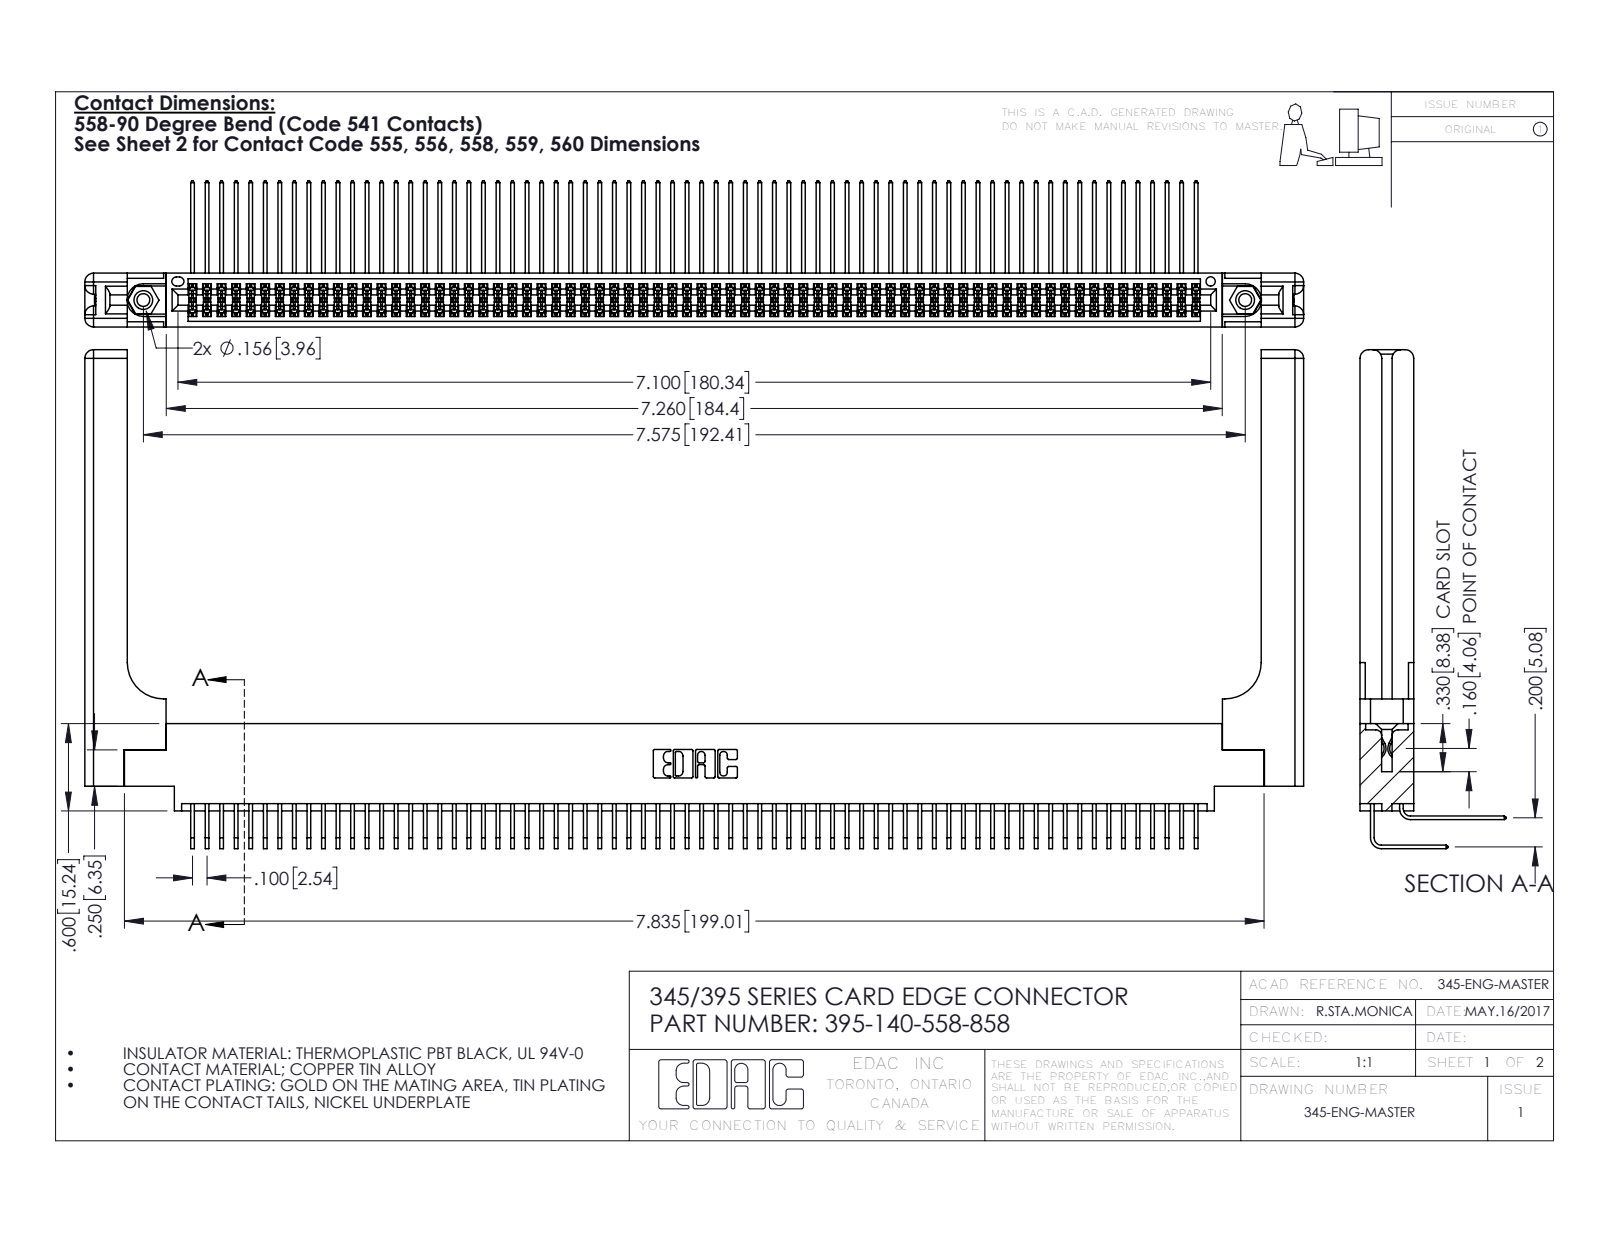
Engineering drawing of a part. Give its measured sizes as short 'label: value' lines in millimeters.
name: 345-250-001_345-250-001-102; 345-220-058_345-220-058; 395-140-558-858; 345-292-001_558 Tail - 2 (+2 more)
written by: SolidWorks 2016 (CONFIG_CONTROL_DESIGN)
unit: mm
bodies: 145 solids, 7666 faces (5132 planar, 2474 cylindrical, 60 other)
size: 212.8 × 87.1 × 25.5
volume: 30 100 mm³; area: 41 510 mm²
holes: 2× ⌀2.3, 2× ⌀3.2, 2× ⌀4, 1× ⌀1.6
bosses: 2× ⌀3.9
rounds: 279× R0.2, 22× R0.3, 16× R1.5, 6× R0.2, 6× R0.8, 3× R0.7, 2× R0.4, 2× R0.5
face distances: 1.8, 7.6, 9.4, 5.1, 2.5, 6.9, 0.6, 5.7, 4.4, 0.6
hole spacings: 6.9, 186.4, 192.4
